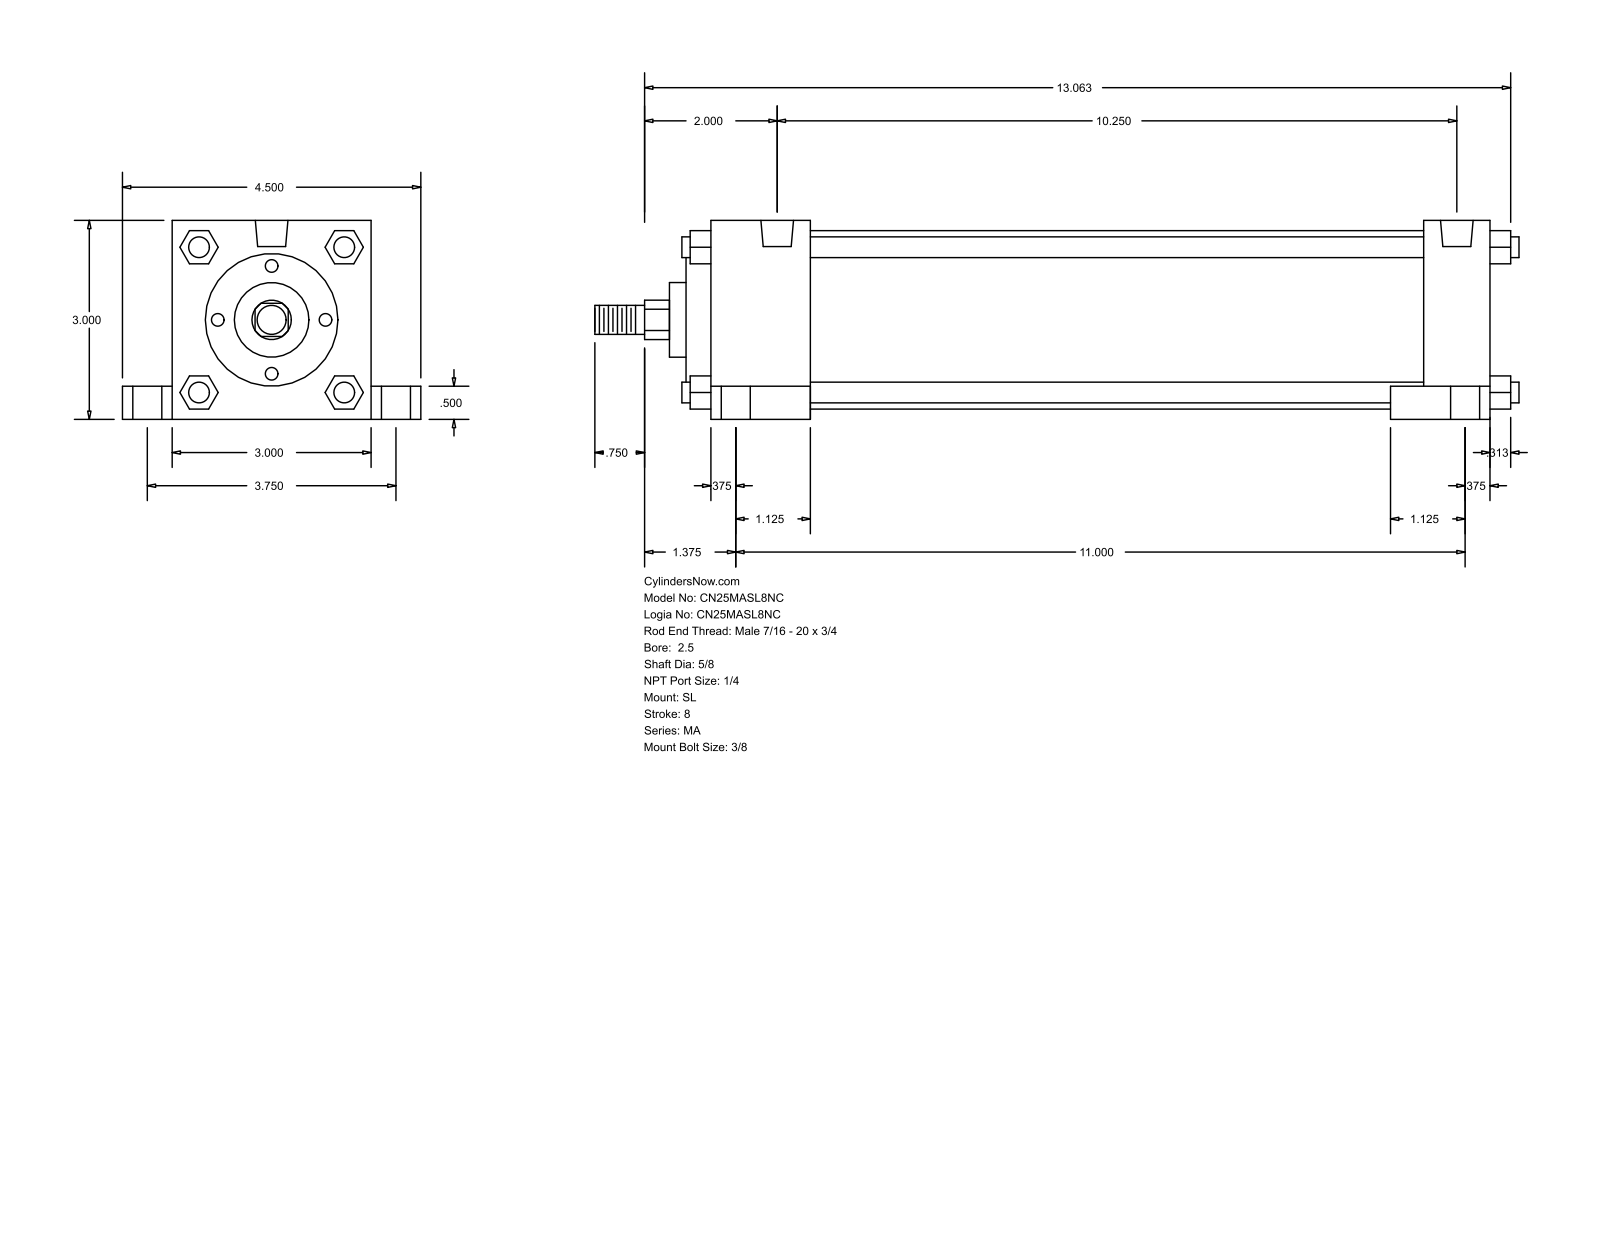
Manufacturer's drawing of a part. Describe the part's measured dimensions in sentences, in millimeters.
The part is named "MA_SL__0250_0.625". Its 3-D file was written by "GSSL Pune (CONFIG_CONTROL_DESIGN)". It is 0 solids with 150 faces: 113 planar, 37 cylindrical and 0 other. Overall it measures 354.01 by 114.3 by 76.2 millimeters. Round holes: 4 of diameter 7.94, 4 of diameter 11.11, 4 of diameter 17.46, 2 of diameter 12.49. Round bosses or shafts: 4 of diameter 7.94, 1 of diameter 68.33, 1 of diameter 50.8, 1 of diameter 28.57, 1 of diameter 15.88, 1 of diameter 11.11. Partial cylindrical surfaces (rounded edges, fillets, slot ends): 1 of radius 7.54. The main face-to-face distances are 76.2, 298.45, 12.7, 234.95, 25.4, 38.1, 260.35, 273.05, 19.05, 63.5. The hole center spacings are 47.73, 50.2, 95.24, 260.35, 267.79, 279.4, 280.3, 295.19.
